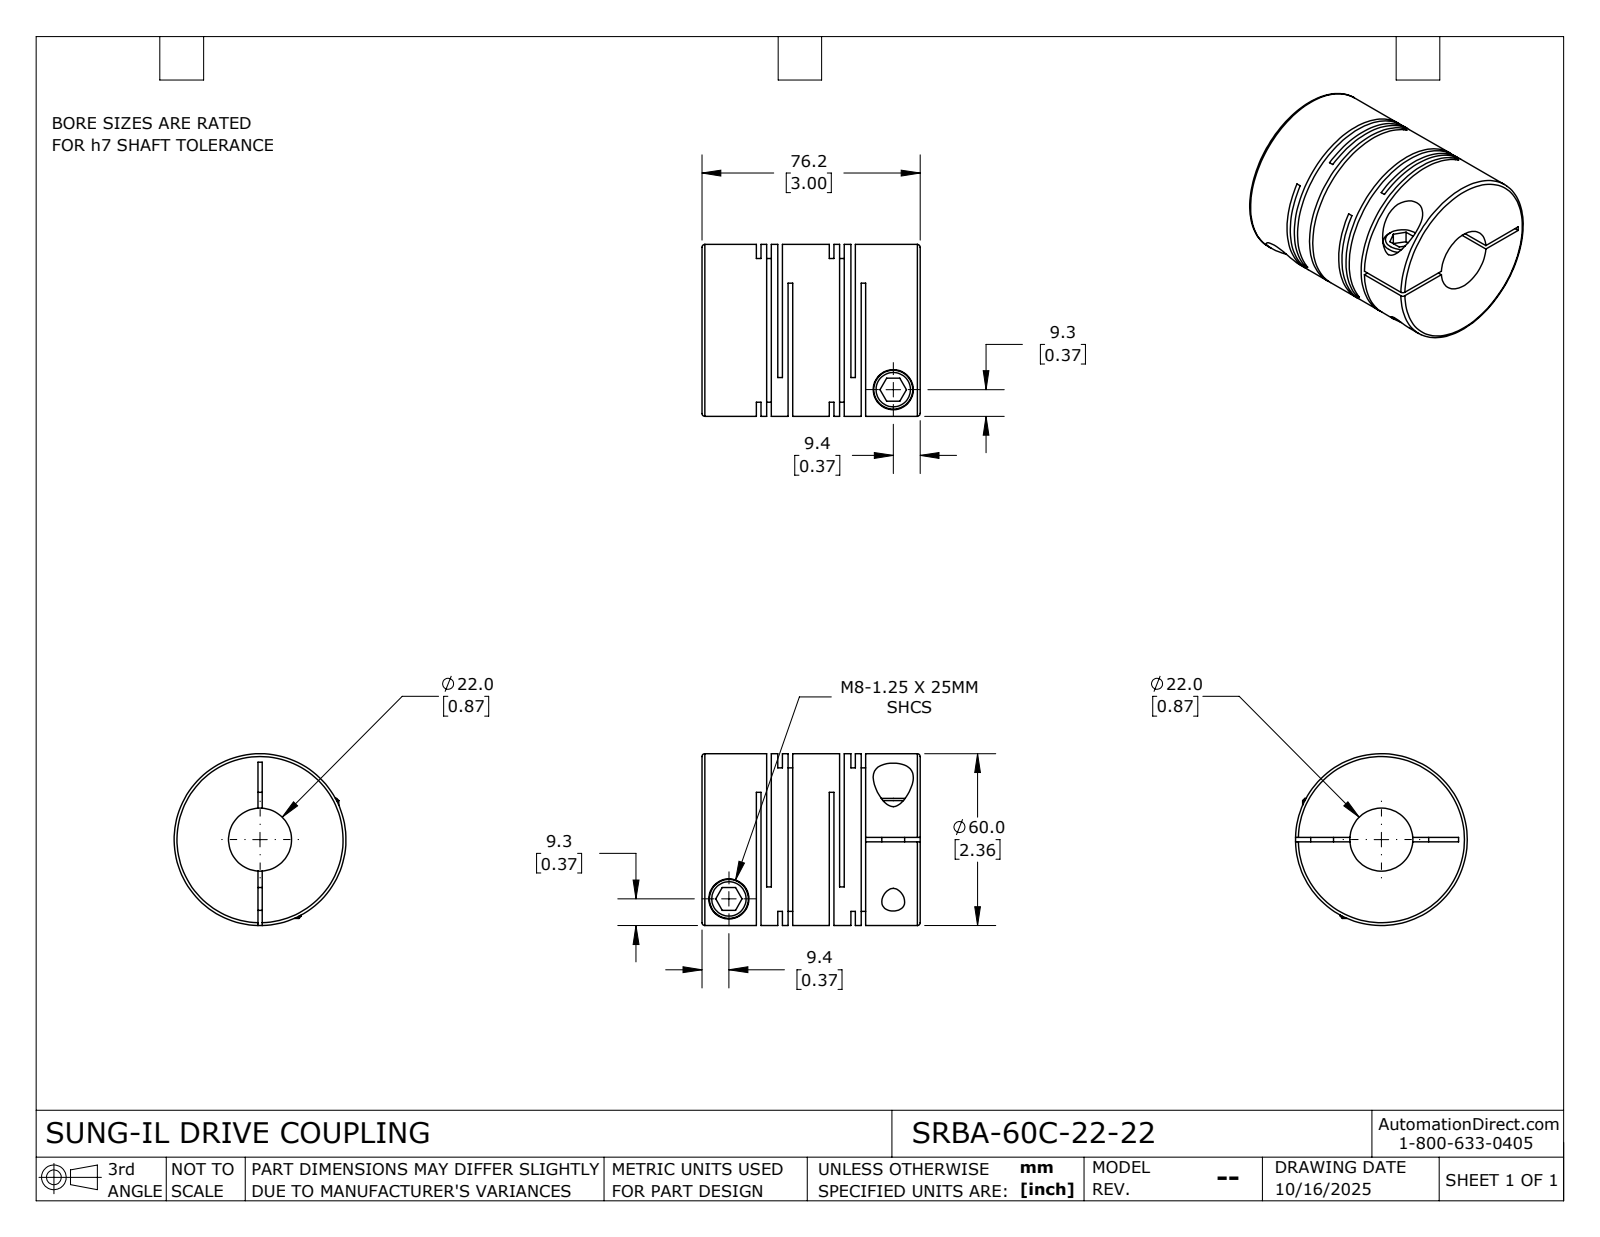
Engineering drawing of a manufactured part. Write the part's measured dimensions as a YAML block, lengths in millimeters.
part_name: "SRBA-60C-22-22"
step_written_by: "SolidWorks 2024 (CONFIG_CONTROL_DESIGN)"
units: millimeters
bodies: {solids: 1, faces: 115, planar: 60, cylindrical: 42, other: 13}
overall_size: [76.2, 60, 60]
volume: 156209
surface_area: 58192
round_holes:
  - {diameter: 8, count: 2}
  - {diameter: 14, count: 2}
  - {diameter: 22, count: 1}
round_bosses_or_shafts:
  - {diameter: 13.6, count: 2}
  - {diameter: 60, count: 1}
face_to_face_distances: [1.6, 3.6, 7.5, 25.5, 33, 2, 5.9, 3.9, 23.9, 21.9]
